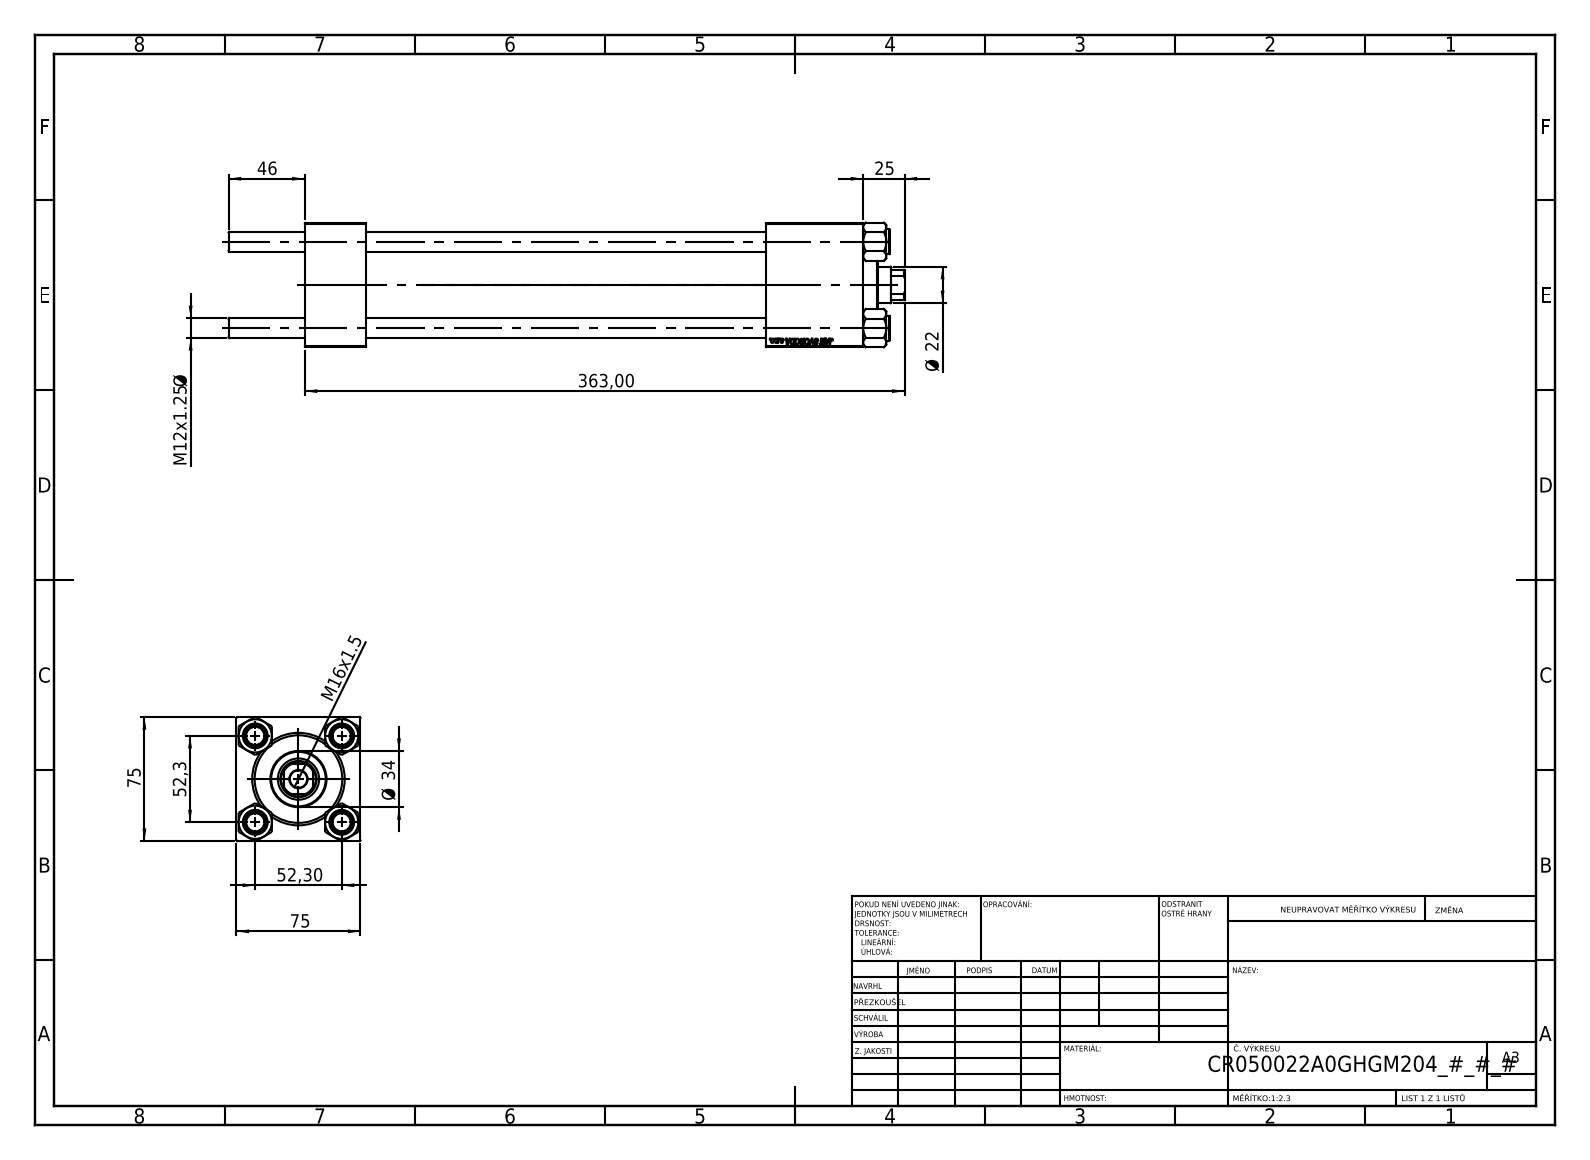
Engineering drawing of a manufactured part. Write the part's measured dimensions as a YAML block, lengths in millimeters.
part_name: "CR025_012_A_0_G_A_G_M_020_+#_##_TYCINKA; V215CR_BODY_A; V215CR_VCP; NUT_M5 (+1 more)"
step_written_by: "SolidWorks 2019 (CONFIG_CONTROL_DESIGN)"
units: millimeters
bodies: {solids: 11, faces: 1134, planar: 520, cylindrical: 78, other: 536}
overall_size: [409, 75.54, 75]
volume: 935184
surface_area: 265480
round_holes:
  - {diameter: 12, count: 4}
  - {diameter: 7, count: 2}
  - {diameter: 20.96, count: 2}
  - {diameter: 30, count: 2}
  - {diameter: 10.5, count: 1}
  - {diameter: 22, count: 1}
  - {diameter: 25, count: 1}
  - {diameter: 41, count: 1}
  - {diameter: 50, count: 1}
  - {diameter: 53, count: 1}
round_bosses_or_shafts:
  - {diameter: 15, count: 4}
  - {diameter: 56, count: 1}
  - {diameter: 34, count: 1}
partial_cylinders:
  - {radius: 10.5, count: 1}
face_to_face_distances: [75, 37, 338, 301, 279, 242, 59, 309.3, 272.3, 30.3]
hole_center_spacings: [36.98, 52.3, 73.96, 277.5]
